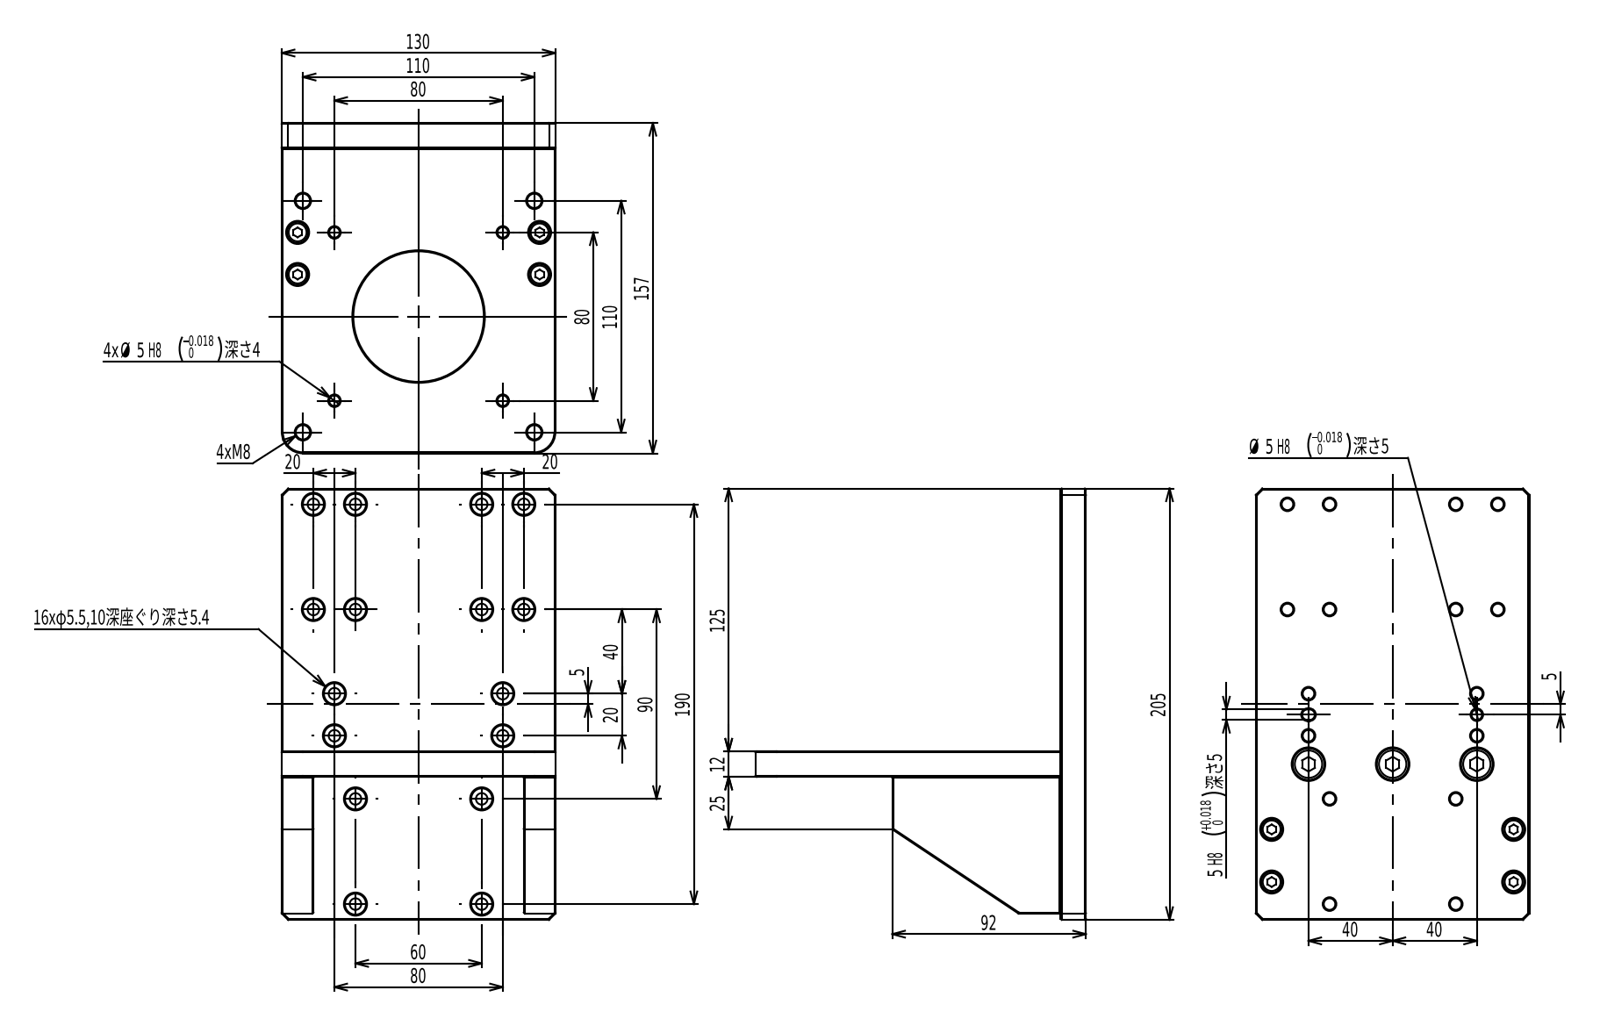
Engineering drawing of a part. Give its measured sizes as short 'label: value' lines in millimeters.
name: PDG130-6
written by: SolidWorks 2020 (CONFIG_CONTROL_DESIGN)
unit: mm
bodies: 15 solids, 653 faces (247 planar, 208 cylindrical, 198 other)
size: 205 × 157 × 130
volume: 611 089 mm³; area: 141 491 mm²
holes: 24× ⌀5.5, 24× ⌀10, 8× ⌀4.2, 7× ⌀5, 7× ⌀6.8, 3× ⌀9, 3× ⌀15, 1× ⌀62
bosses: 8× ⌀8.5, 8× ⌀4.13, 3× ⌀13, 3× ⌀7
rounds: 4× R2.5, 2× R10
face distances: 12, 15, 115, 130, 100, 80, 5.4, 6.6, 137, 125
hole spacings: 80, 20, 96.18, 80.62, 50, 41.23, 90.55, 110
